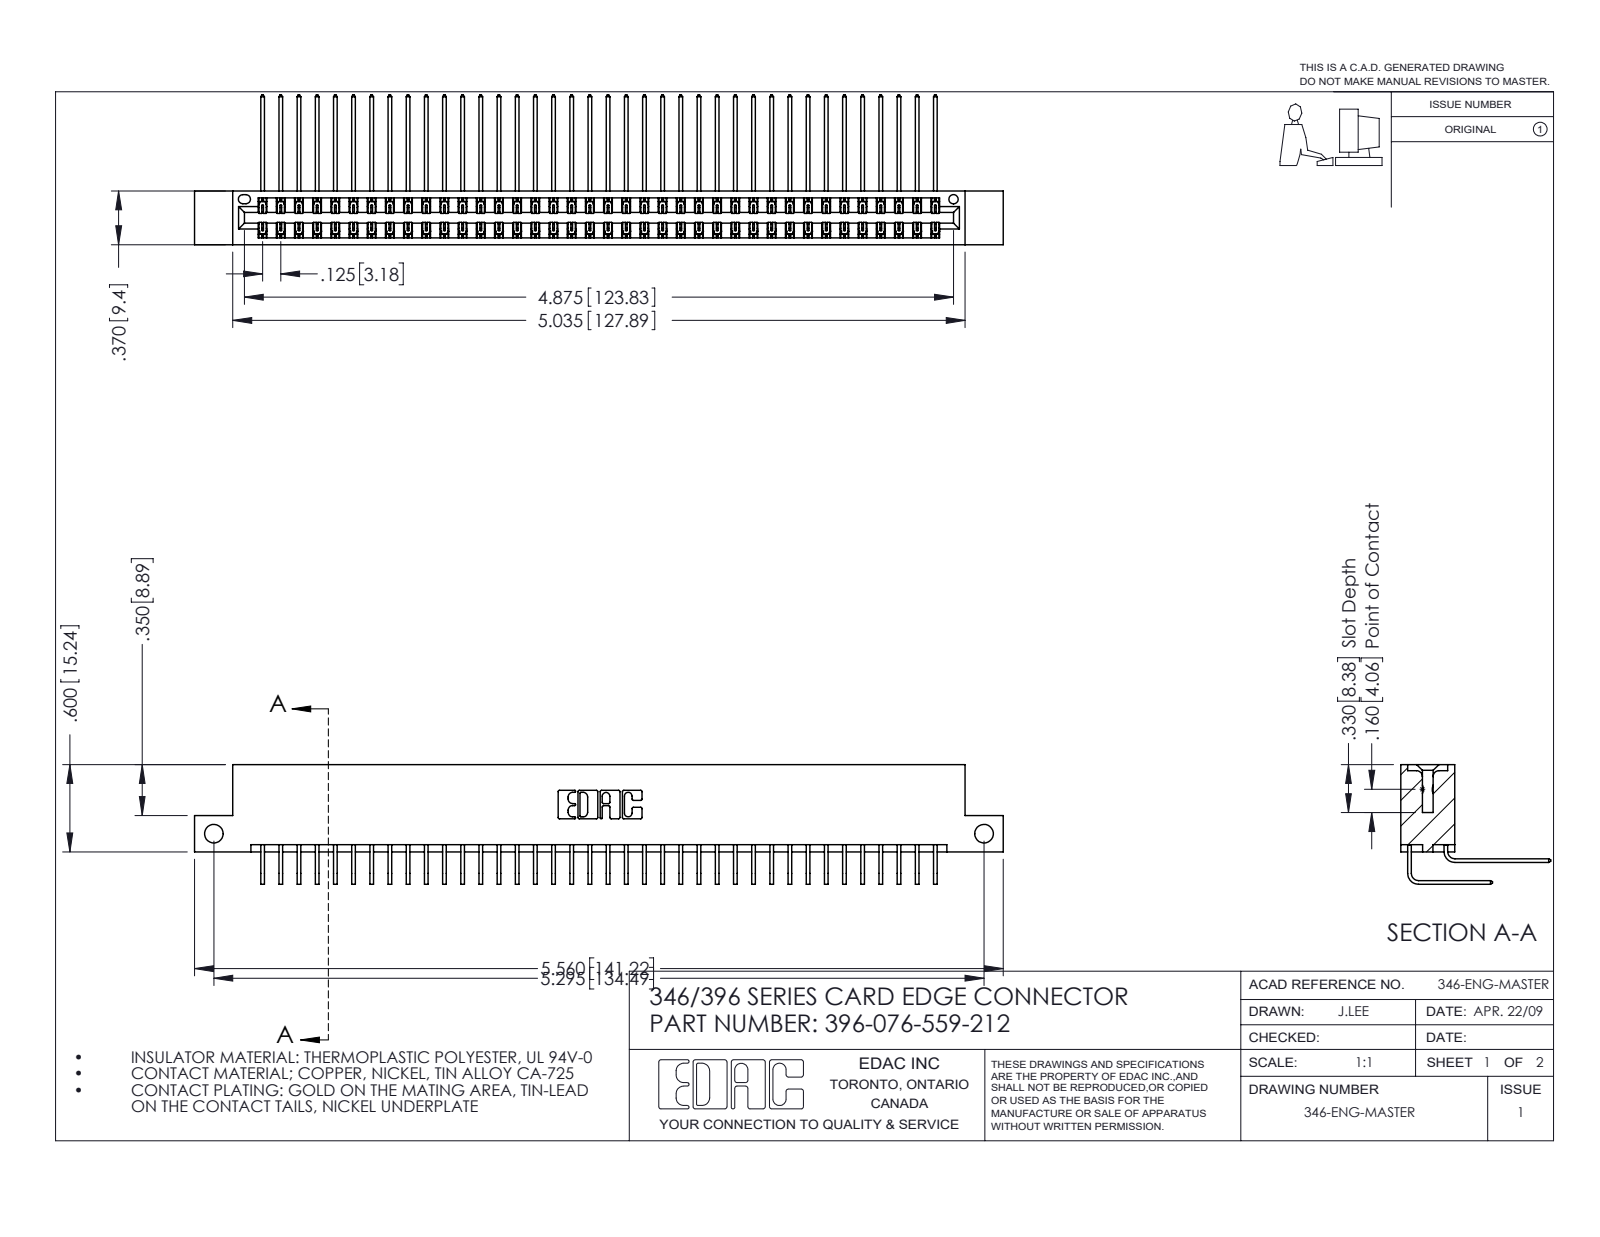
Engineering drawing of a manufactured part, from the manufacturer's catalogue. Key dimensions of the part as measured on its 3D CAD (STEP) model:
Part name (STEP PRODUCT): 345-292-001_559 Tail - 2; 396-076-559-212; 345-292-001_558 559 Tail - 1; 346 Part_Flush Mounting Lugs - Side Mount
STEP written by: SolidWorks 2016 (CONFIG_CONTROL_DESIGN)
Units: inches
Bodies: 77 solids, 4226 faces (2888 planar, 1338 cylindrical, 0 other)
Overall size (bounding box): 5.56 × 1.03 × 0.823
Volume: 0.86 in³ · Surface area: 32.97 in²
Round holes (diameter × count): ⌀0.128 ×2, ⌀0.064 ×1
Partial cylindrical surfaces — rounded edges, fillets, slot ends (radius × count): R0.006 ×114, R0.01 ×22, R0.007 ×6, R0.031 ×6, R0.026 ×3, R0.014 ×2, R0.022 ×2, R0.024 ×2
Main face-to-face distances: 0.048, 0.322, 0.025, 0.37, 0.25, 0.072, 0.298, 0.275, 0.148, 0.222
Hole centre spacings: 5.295
